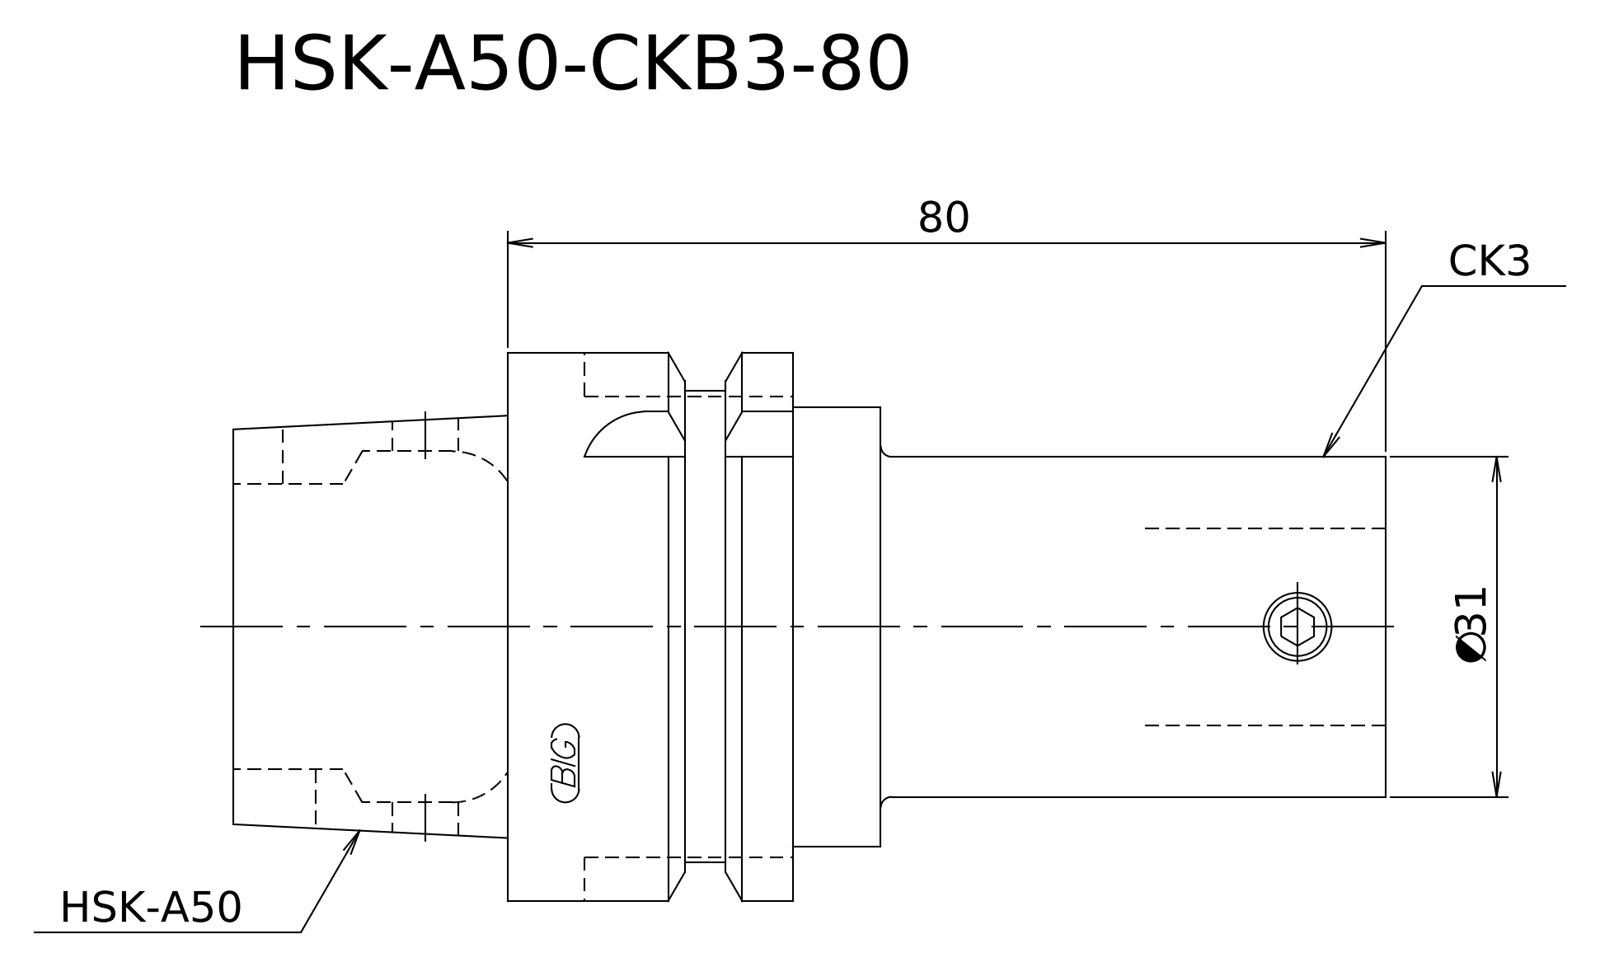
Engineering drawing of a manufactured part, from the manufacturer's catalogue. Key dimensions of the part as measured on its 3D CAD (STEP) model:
STEP written by: Kubotek KeyCreator V8.5.1 (14335) (CONFIG_CONTROL_DESIGN)
Units: millimetres
Bodies: 1 solid, 17 faces (7 planar, 6 cylindrical, 4 other)
Overall size (bounding box): 105 × 50 × 50
Volume: 120 606 mm³ · Surface area: 16 823 mm²
Round bosses / shafts (diameter × count): ⌀50 ×1, ⌀43 ×1, ⌀40 ×1, ⌀38.3 ×1, ⌀31 ×1
Main face-to-face distances: 25, 80, 105, 54, 26, 51, 46, 8, 34, 59
